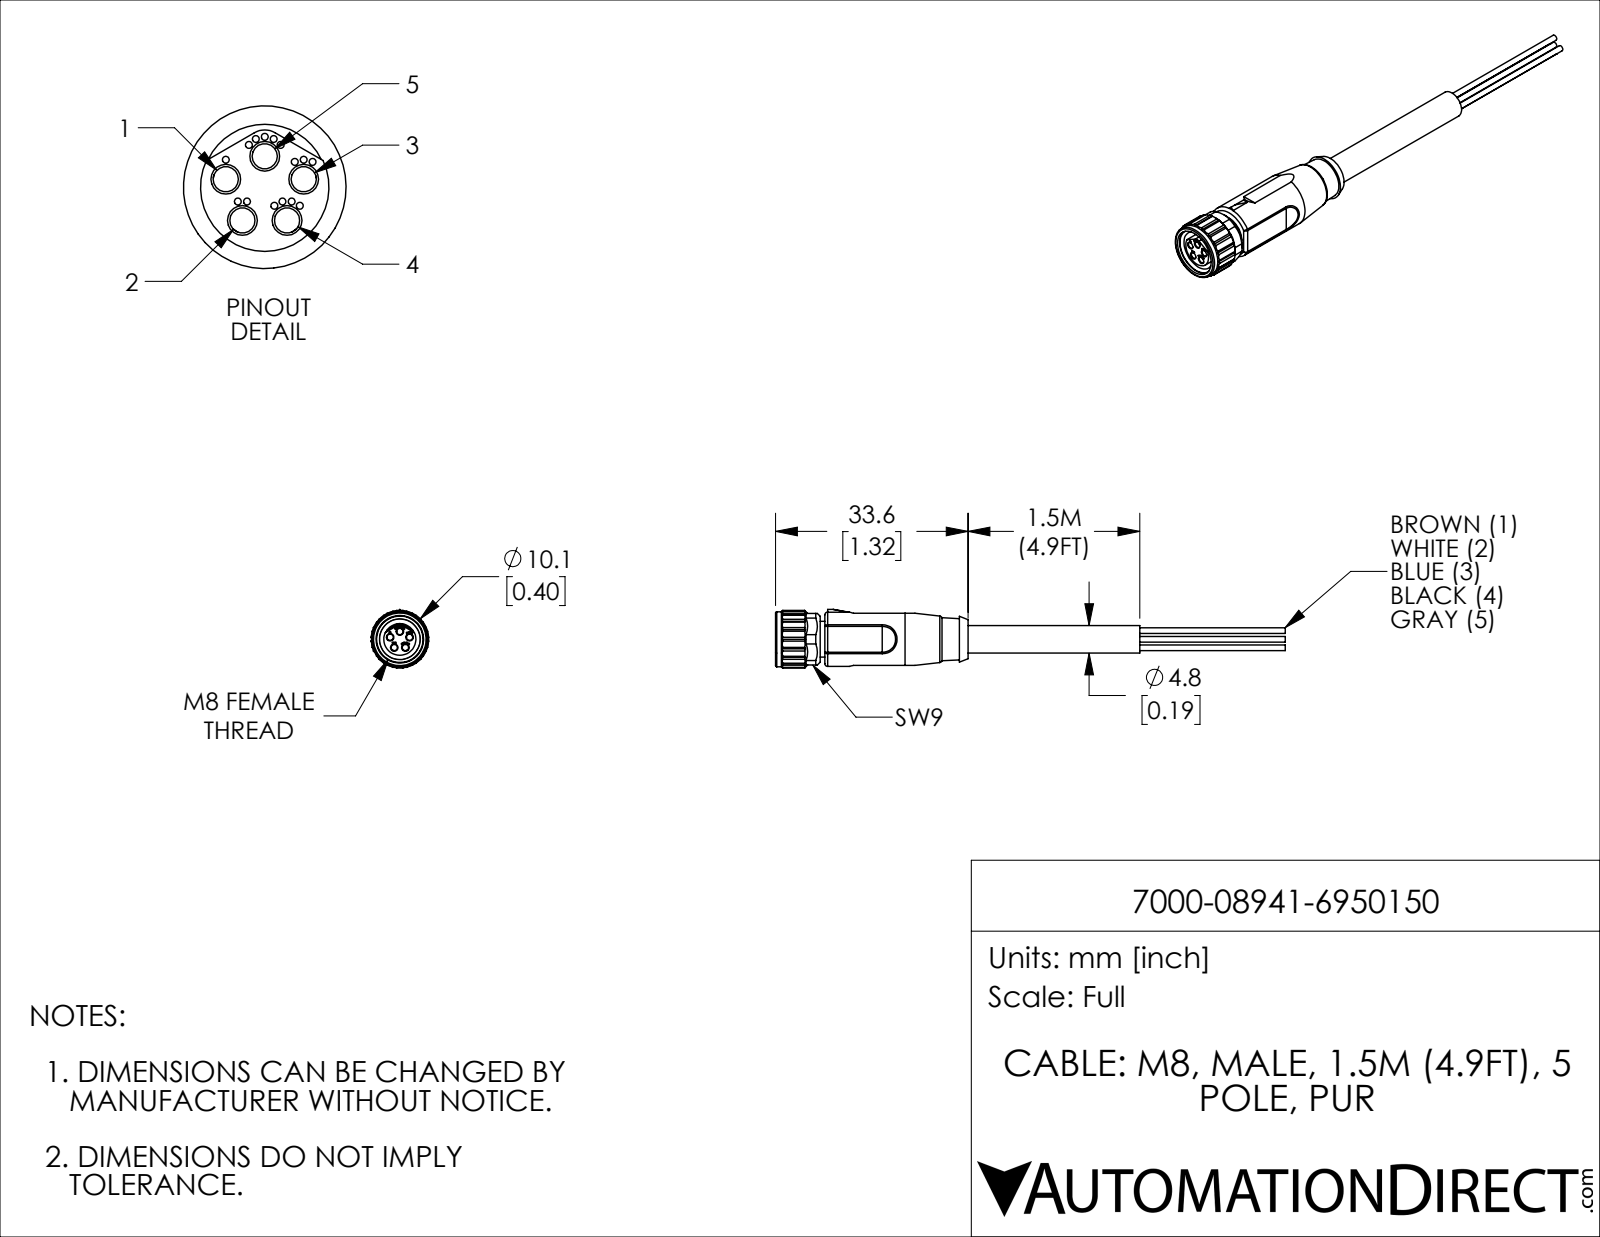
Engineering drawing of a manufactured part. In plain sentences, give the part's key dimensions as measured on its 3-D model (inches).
The part is named "7000-08941-6950150". Its 3-D file was written by "SolidWorks 2019 (CONFIG_CONTROL_DESIGN)". It is 1 solid with 285 faces: 111 planar, 127 cylindrical and 47 other. Overall it measures 3.504 by 0.402 by 0.397 inches. Its volume is 0.16 cubic inches and its surface area 3.561 square inches. Round holes: 15 of diameter 0.012, 5 of diameter 0.043, 1 of diameter 0.241, 1 of diameter 0.28, 1 of diameter 0.327. Round bosses or shafts: 5 of diameter 0.039, 1 of diameter 0.378, 1 of diameter 0.374, 1 of diameter 0.246, 1 of diameter 0.189. Partial cylindrical surfaces (rounded edges, fillets, slot ends): 18 of radius 0.079, 6 of radius 0.02, 6 of radius 0.03, 4 of radius 0.033, 2 of radius 0.008, 2 of radius 0.197, 1 of radius 0.035, 1 of radius 0.09. The main face-to-face distances are 0.323, 0.358, 0.357, 0.031, 1.016, 0.984, 0.354, 0.28, 0.311, 1.295. The hole center spacings are 0.033, 0.016, 0.078, 0.031, 0.044, 0.069, 0.077, 0.099.
